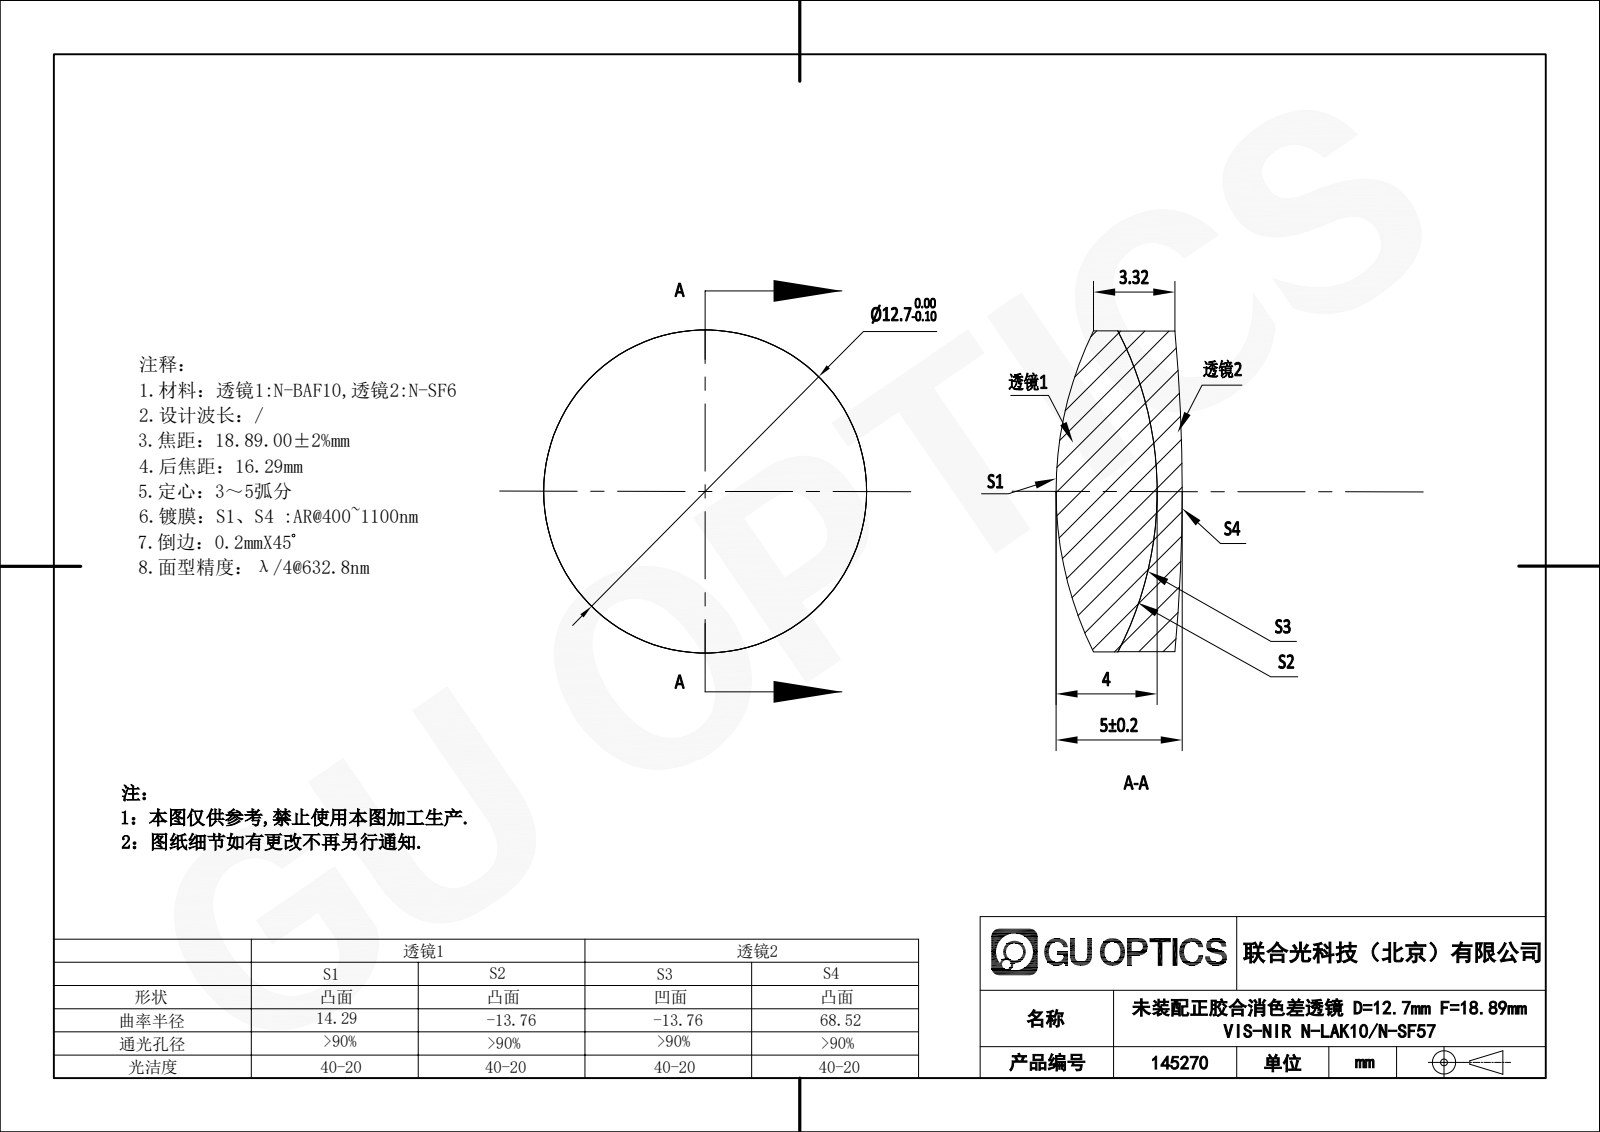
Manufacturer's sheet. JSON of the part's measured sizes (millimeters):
{"part_name": "145270b; 145270a", "step_written_by": "SolidWorks 2020 (CONFIG_CONTROL_DESIGN)", "units": "millimeters", "bodies": {"solids": 2, "faces": 12, "planar": 0, "cylindrical": 4, "other": 8}, "overall_size": [12.7, 12.7, 5], "volume_mm3": 522, "surface_area_mm2": 657, "round_bosses_or_shafts": [[12.7, 1], [12.69, 1]]}
